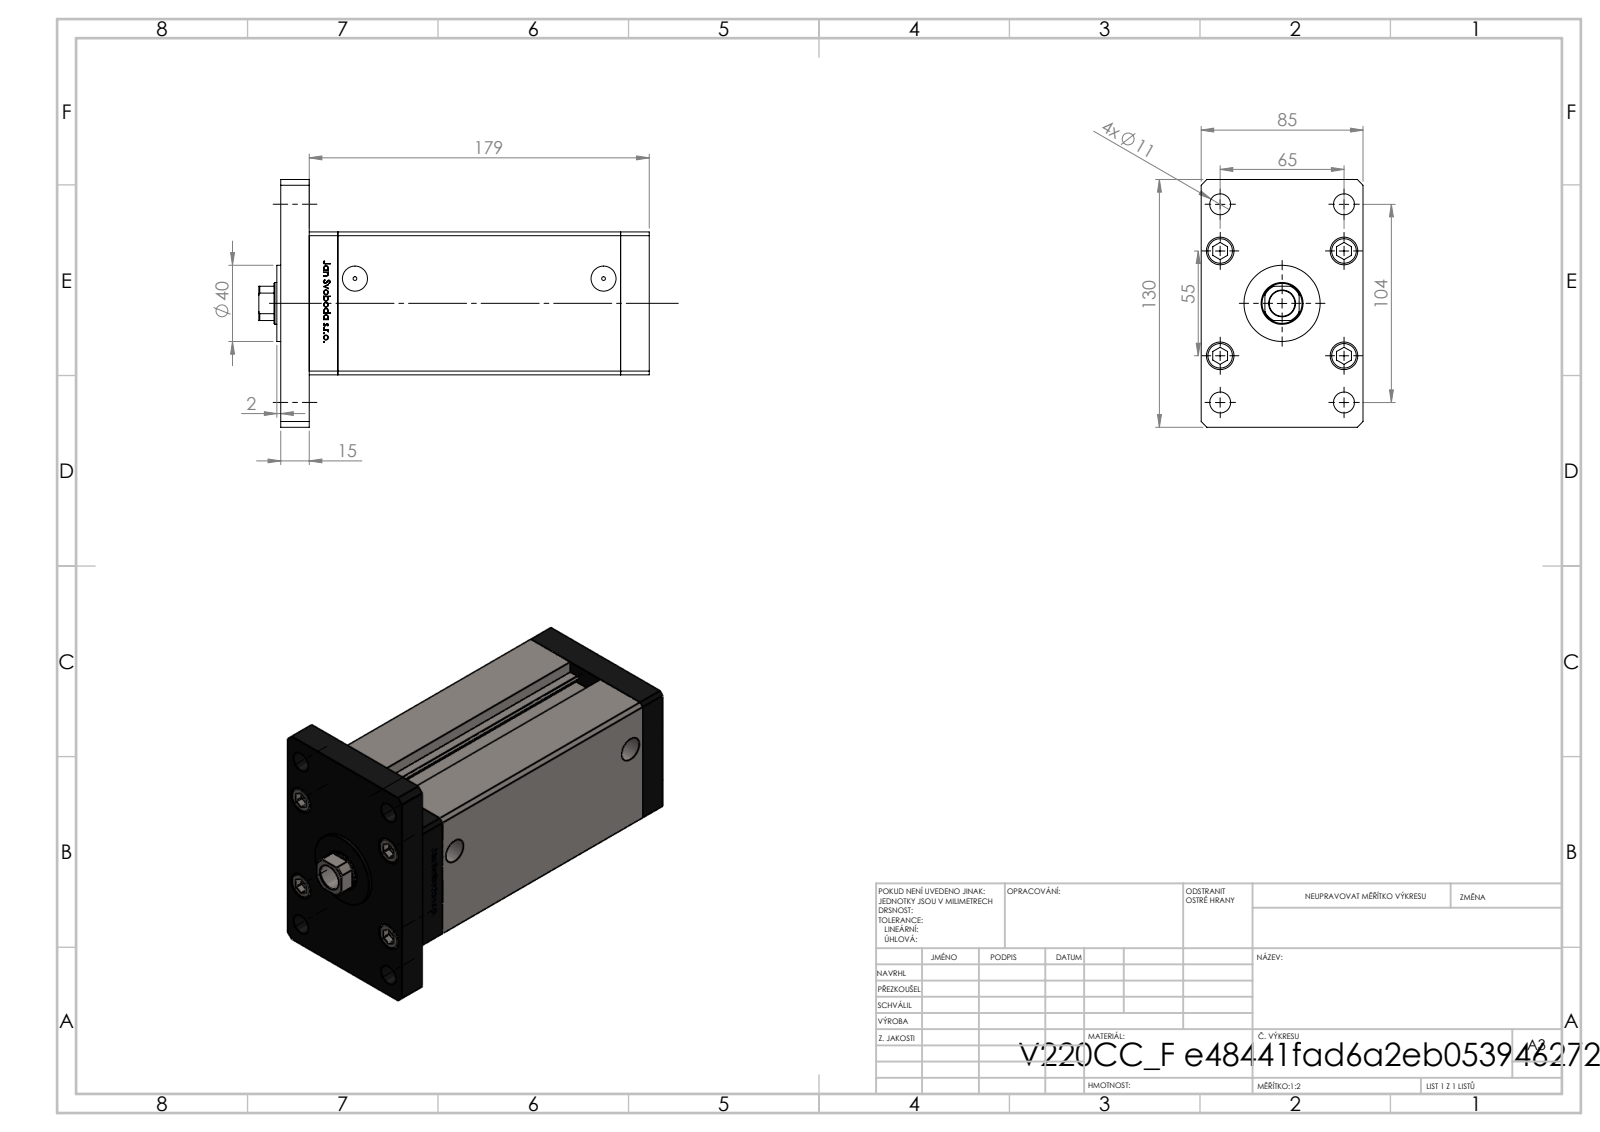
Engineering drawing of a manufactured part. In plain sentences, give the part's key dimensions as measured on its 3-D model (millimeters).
The part is named "ALLEN BOLT; V220C BACK_F; V220C_F_MIDDLE; V220C_F (+2 more)". Its 3-D file was written by "SolidWorks 2019 (CONFIG_CONTROL_DESIGN)". It is 19 solids with 1308 faces: 515 planar, 187 cylindrical and 606 other. Overall it measures 205 by 130 by 85 millimeters. Its volume is 1 165 000 cubic millimeters and its surface area 198 848 square millimeters. Round holes: 9 of diameter 11, 5 of diameter 15.5, 4 of diameter 10, 4 of diameter 14.5, 2 of diameter 2, 2 of diameter 13.16, 1 of diameter 13.5, 1 of diameter 22, 1 of diameter 23.5. Round bosses or shafts: 9 of diameter 8, 5 of diameter 14.5, 1 of diameter 40. Partial cylindrical surfaces (rounded edges, fillets, slot ends): 2 of radius 0.93, 1 of radius 10.5. The main face-to-face distances are 15, 85, 163.5, 178.5, 75, 148.5, 30, 193.5, 10.5, 27.5. The hole center spacings are 28, 24.5, 42.57, 61.32, 65, 69.46, 79.5, 102.69.
